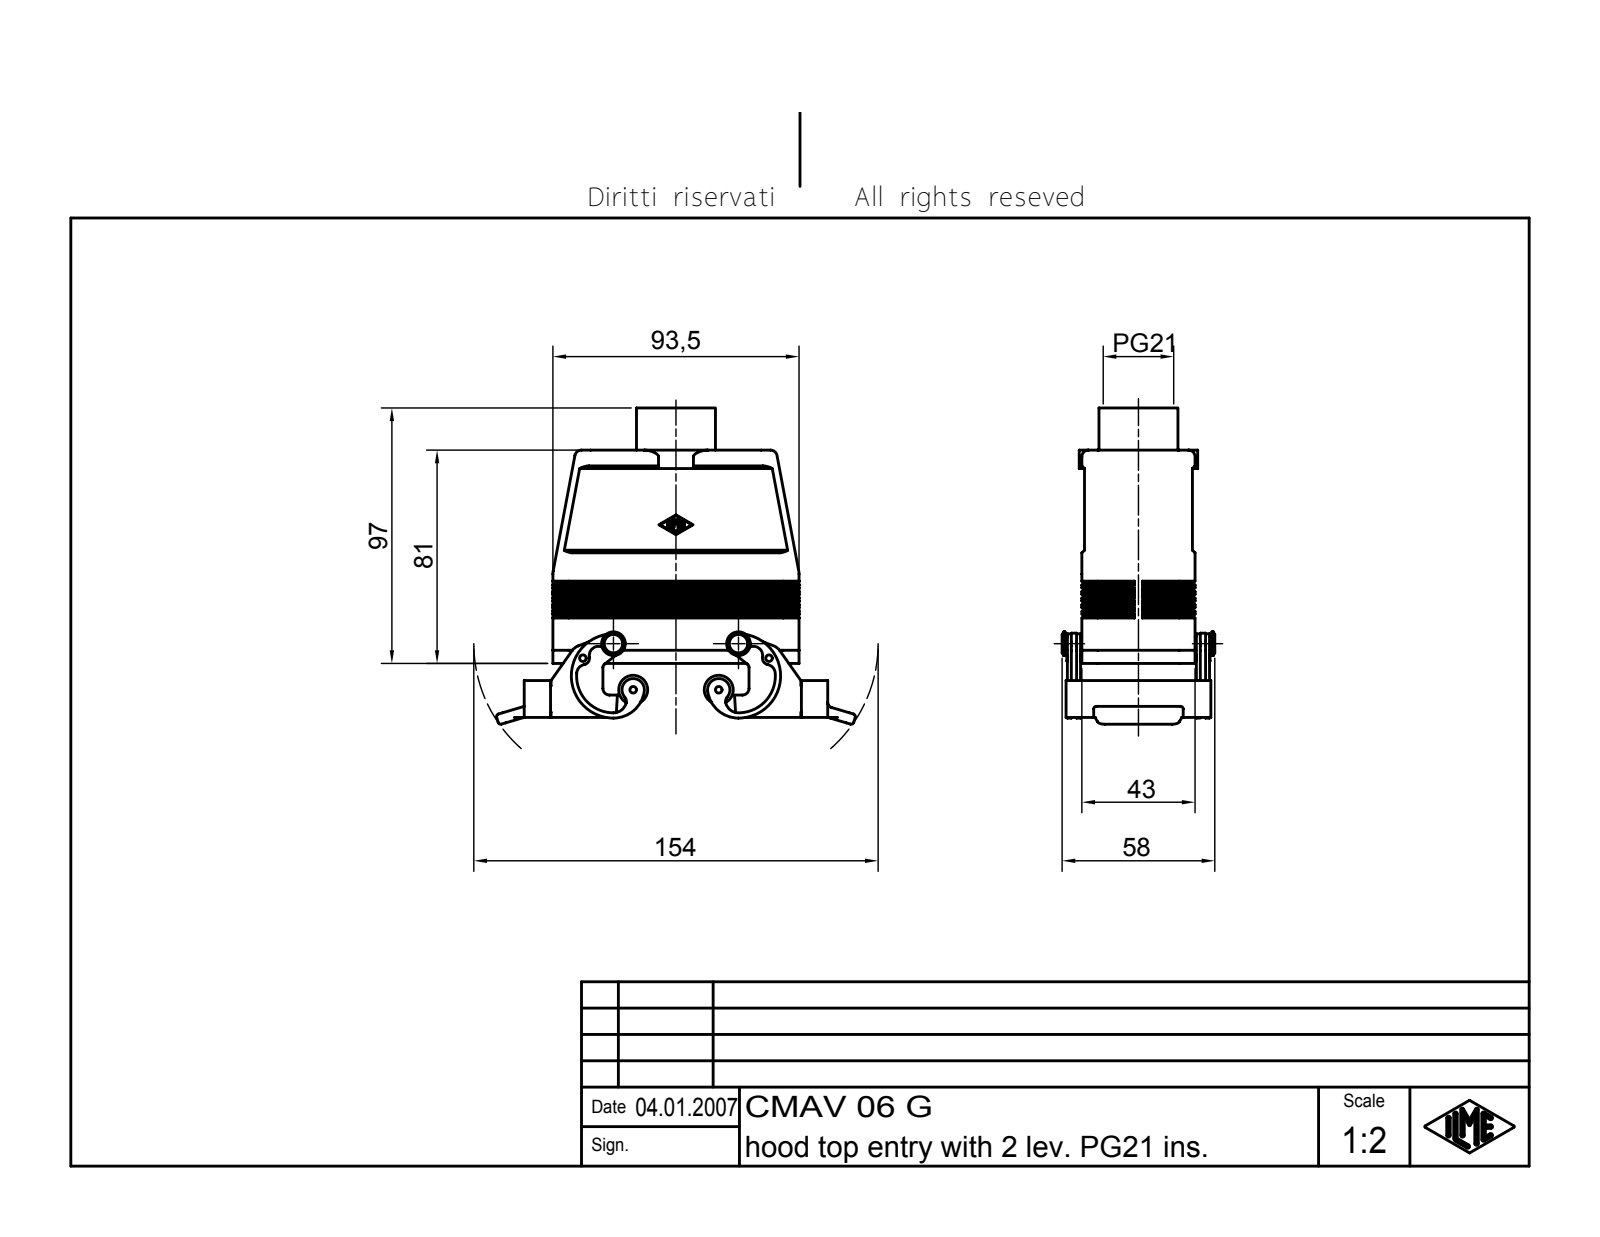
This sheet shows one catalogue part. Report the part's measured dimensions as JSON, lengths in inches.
{"part_name": "CAV Tüllengehäuse 2 Bügel für einen Einsatz", "step_written_by": "Autodesk Inventor 7 (AUTOMOTIVE_DESIGN)", "units": "inches", "bodies": {"solids": 1, "faces": 965, "planar": 302, "cylindrical": 256, "other": 407}, "overall_size": [5.366, 4.728, 2.283], "volume_in3": 6.915, "surface_area_in2": 100.4, "round_holes": [[0.098, 2], [0.976, 1], [1.054, 1]], "round_bosses_or_shafts": [[0.433, 2], [0.354, 2], [0.197, 2], [0.079, 2], [1.772, 1], [1.181, 1]], "partial_cylinders_radius": [[0.01, 14], [0.039, 12], [0.098, 10], [0.236, 10], [0.118, 8], [0.079, 7], [0.138, 4], [0.197, 4]], "face_to_face_distances": [0.157, 0.118, 1.535, 1.378, 1.496, 0.039, 1.654, 1.693, 1.614, 0.079], "hole_center_spacings": [2.783]}
